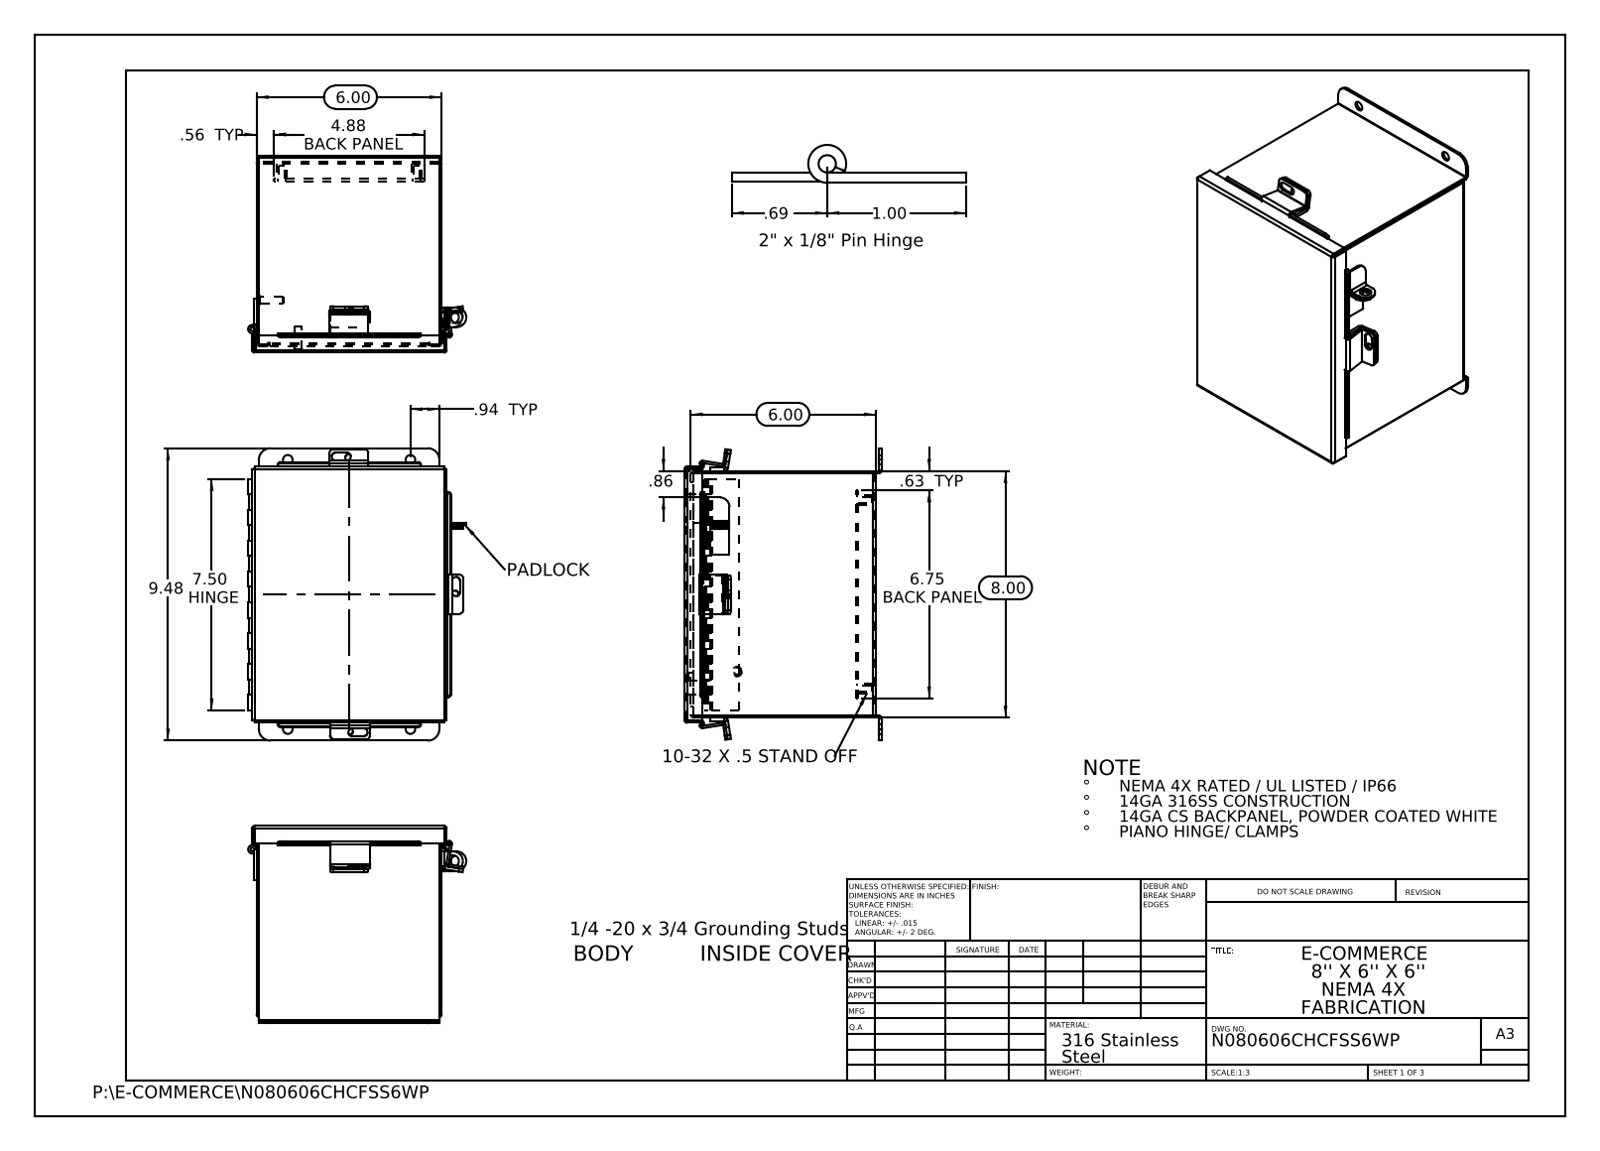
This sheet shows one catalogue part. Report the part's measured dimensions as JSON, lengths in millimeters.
{"part_name": "N080606CHCFSS6WP JIC Enclosure Template; N080606CHCFSS6WP _JIC Hinge; N080606CHCFSS6WP JIC Clamp Bracket; N080606CHCFSS6WP JIC Top (+8 more)", "step_written_by": "SolidWorks 2013 (CONFIG_CONTROL_DESIGN)", "units": "millimeters", "bodies": {"solids": 21, "faces": 584, "planar": 363, "cylindrical": 201, "other": 20}, "overall_size": [240.7, 179.6, 162.3], "volume_mm3": 437400, "surface_area_mm2": 474000, "round_holes": [[6.4, 7], [4.7, 4], [7.9, 4], [3.2, 1], [3.2, 1], [9.5, 1], [9.5, 1]], "round_bosses_or_shafts": [[8, 4], [8, 2], [6, 2], [6.9, 1], [6.4, 1]], "partial_cylinders_radius": [[0.3, 13], [0.2, 12], [2.2, 12], [3.2, 10], [2.1, 6], [2.5, 6], [3.4, 6], [9.5, 4]], "face_to_face_distances": [1.9, 150.5, 155.7, 201.3, 152.4, 148.6, 153.7, 157.6, 199.4, 203.2], "hole_center_spacings": [33.4, 111.1, 188.7, 216.4, 101, 111.1, 155.6, 191.2]}
